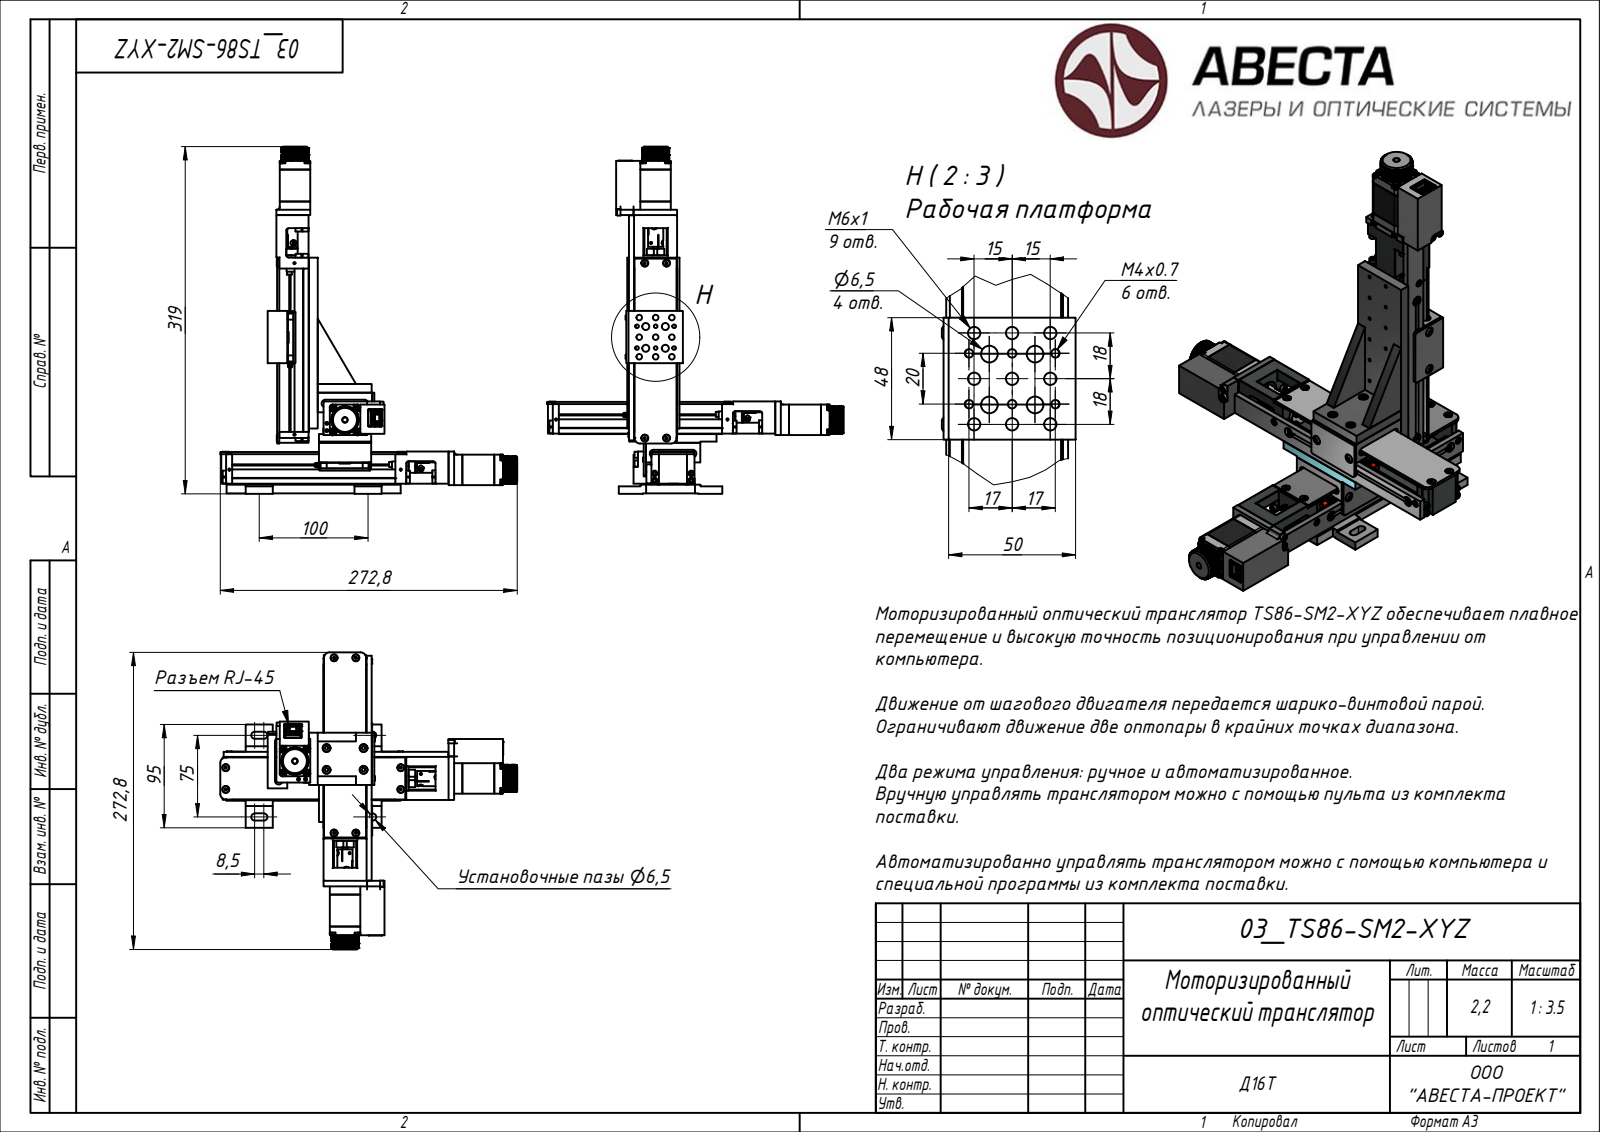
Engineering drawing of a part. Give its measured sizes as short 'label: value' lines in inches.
written by: Rhino 7.34 (AUTOMOTIVE_DESIGN)
unit: in
bodies: 1 solid, 7125 faces (4304 planar, 1964 cylindrical, 857 other)
size: 12.559 × 10.74 × 10.74
volume: 51.66 in³; area: 533.2 in²
holes: 42× ⌀0.134, 30× ⌀0.256, 22× ⌀0.295, 21× ⌀0.097, 21× ⌀0.098, 21× ⌀0.128, 15× ⌀0.041, 13× ⌀0.194, 12× ⌀0.194, 12× ⌀0.197, 9× ⌀0.085, 7× ⌀0.177
bosses: 30× ⌀0.177, 17× ⌀0.217, 15× ⌀0.236, 12× ⌀0.209, 12× ⌀0.118, 12× ⌀0.098, 9× ⌀0.197, 6× ⌀0.276
rounds: 108× R0.02, 30× R0.098, 30× R0.118, 24× R0.079, 12× R0.039, 8× R0.128, 7× R0.048, 7× R0.048
face distances: 1.811, 0.079, 0.02, 0.098, 0.315, 1.083, 1.161, 0.197, 0.965, 1.831
hole spacings: 0.787, 0.709, 1.059, 2.362, 0.039, 1.575, 2.466, 0.394
